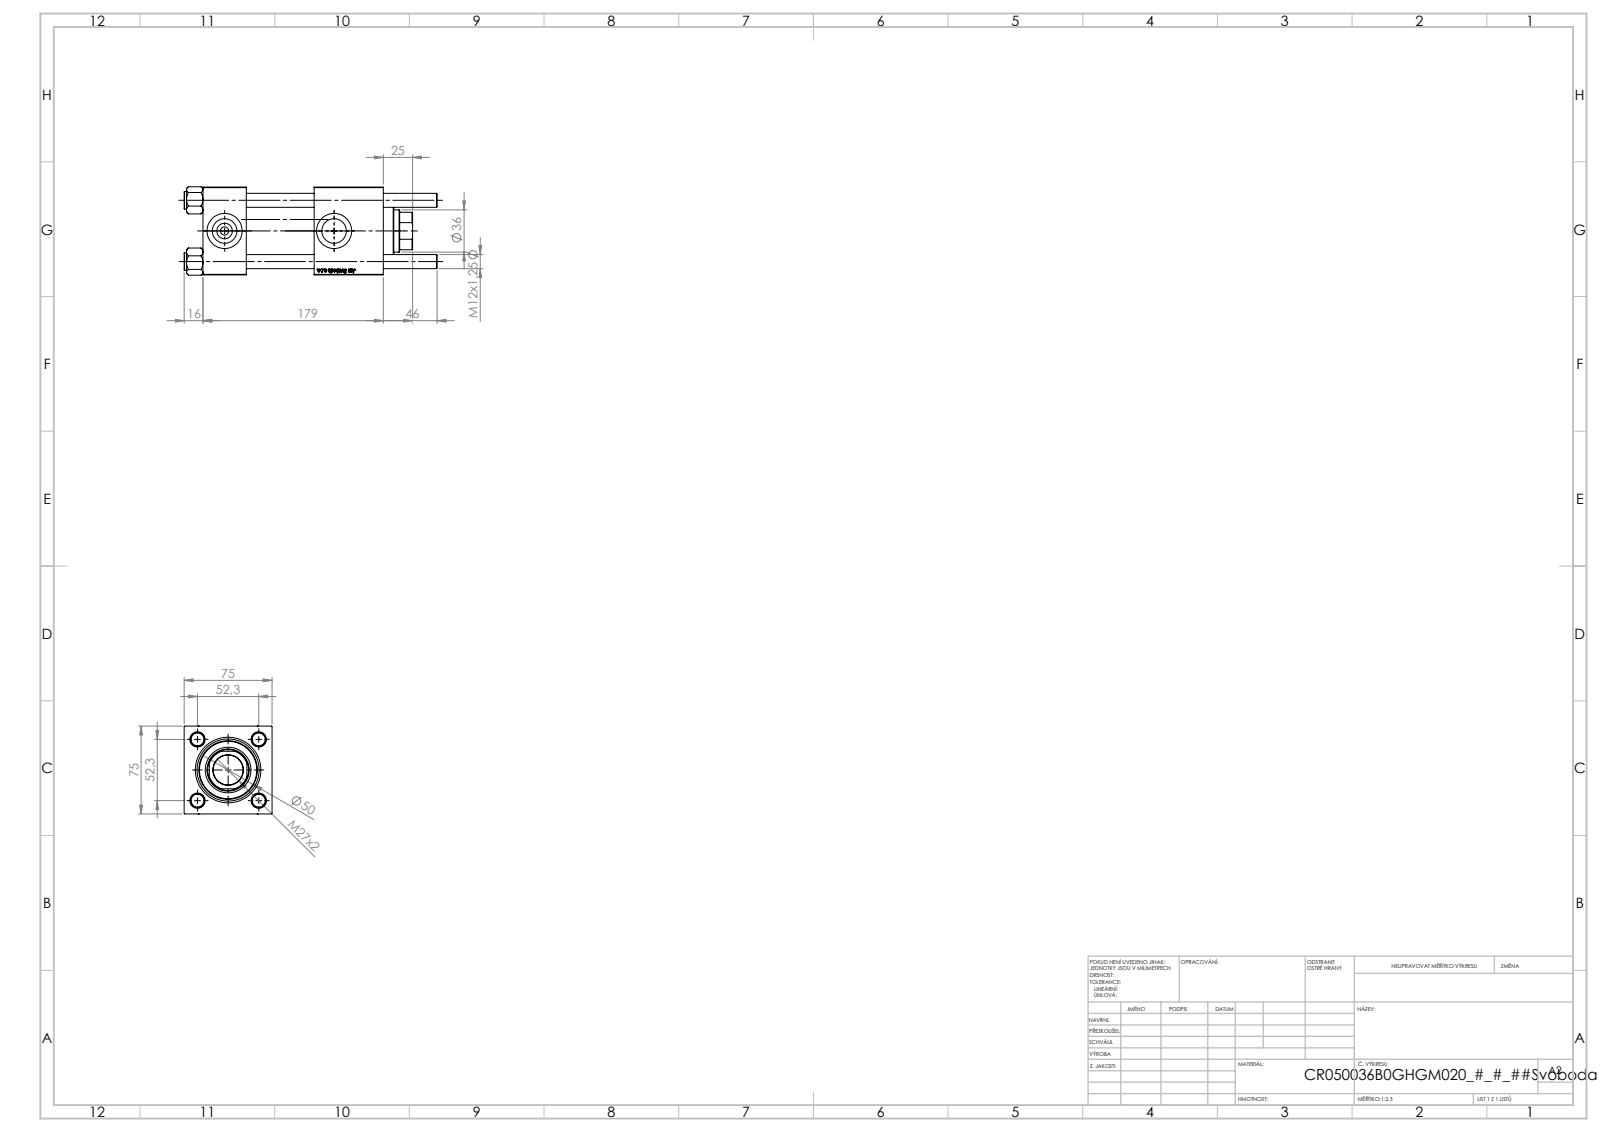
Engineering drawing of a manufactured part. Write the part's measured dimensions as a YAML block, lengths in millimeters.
part_name: "V215CR_VCP_B; V215CR_B_TYCINKA; NUT_M5_B; V215_VC_A (+1 more)"
step_written_by: "SolidWorks 2019 (CONFIG_CONTROL_DESIGN)"
units: millimeters
bodies: {solids: 11, faces: 1158, planar: 432, cylindrical: 78, other: 648}
overall_size: [216, 75.45, 75]
volume: 719229
surface_area: 171694
round_holes:
  - {diameter: 12, count: 4}
  - {diameter: 7, count: 2}
  - {diameter: 20.96, count: 2}
  - {diameter: 30, count: 2}
  - {diameter: 25.5, count: 1}
  - {diameter: 36, count: 1}
  - {diameter: 39, count: 1}
  - {diameter: 41, count: 1}
  - {diameter: 53, count: 1}
round_bosses_or_shafts:
  - {diameter: 15, count: 4}
  - {diameter: 56, count: 1}
  - {diameter: 50, count: 1}
partial_cylinders:
  - {radius: 17.5, count: 1}
face_to_face_distances: [75, 37, 95, 58, 154, 117, 59, 125.3, 88.3, 30.3]
hole_center_spacings: [36.98, 52.3, 73.96, 93.5]
